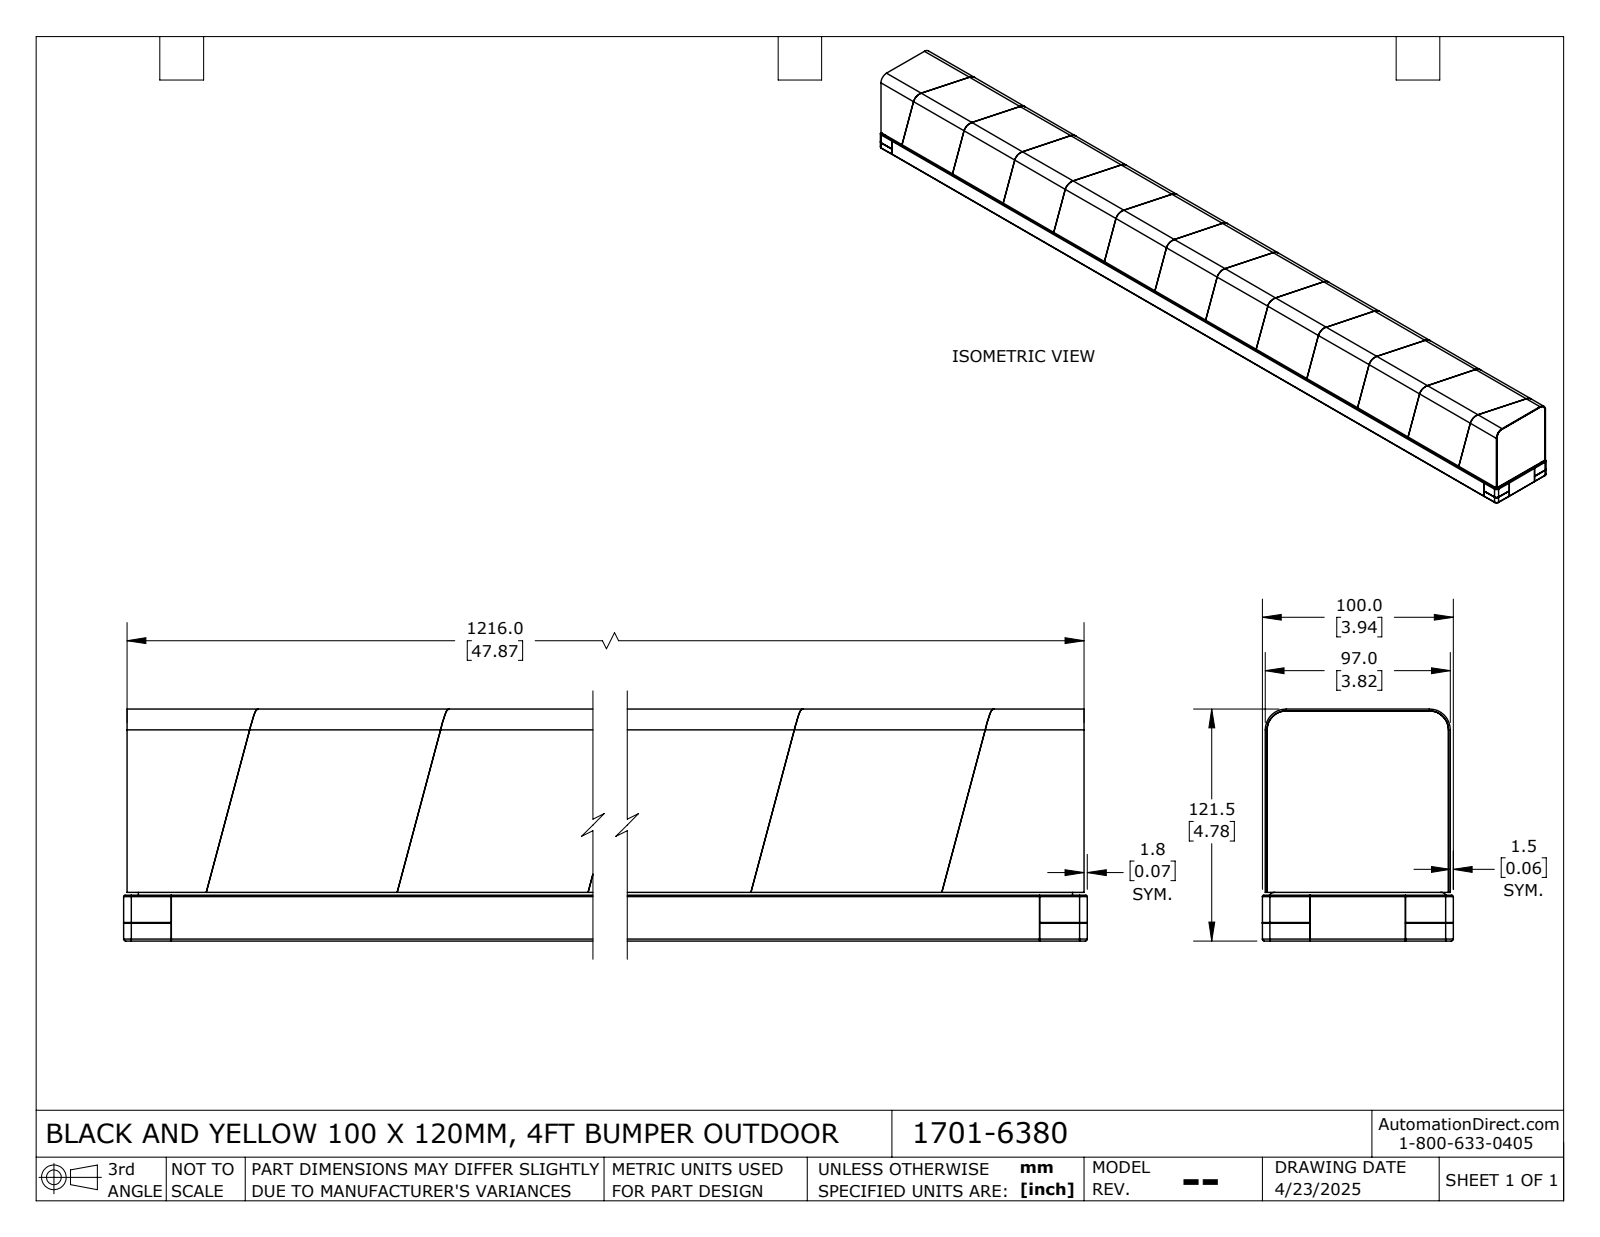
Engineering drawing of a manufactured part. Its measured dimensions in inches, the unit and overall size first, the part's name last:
Units: inches
Overall size (bounding box): 48.012 × 4.783 × 3.937
Round holes (diameter × count): ⌀0.472 ×4
Partial cylindrical surfaces — rounded edges, fillets, slot ends (radius × count): R0.012 ×16, R0.02 ×8, R0.03 ×8, R0.039 ×8, R0.157 ×8, R0.079 ×4, R0.11 ×4, R0.236 ×4
Main face-to-face distances: 0.039, 3.74, 3.78, 0.079, 3.819, 0.925, 3.642, 1.004, 4.744, 4.665
Hole centre spacings: 15.217, 30.433, 45.65
Volume: 739 in³ · Surface area: 3 157 in²
Bodies: 29 solids, 631 faces (375 planar, 176 cylindrical, 80 other)
Part name (STEP PRODUCT): 1701-6380 AD SENTIR bumper 100-120 LO 2_4 ft
STEP written by: SolidWorks 2024 (AUTOMOTIVE_DESIGN)
